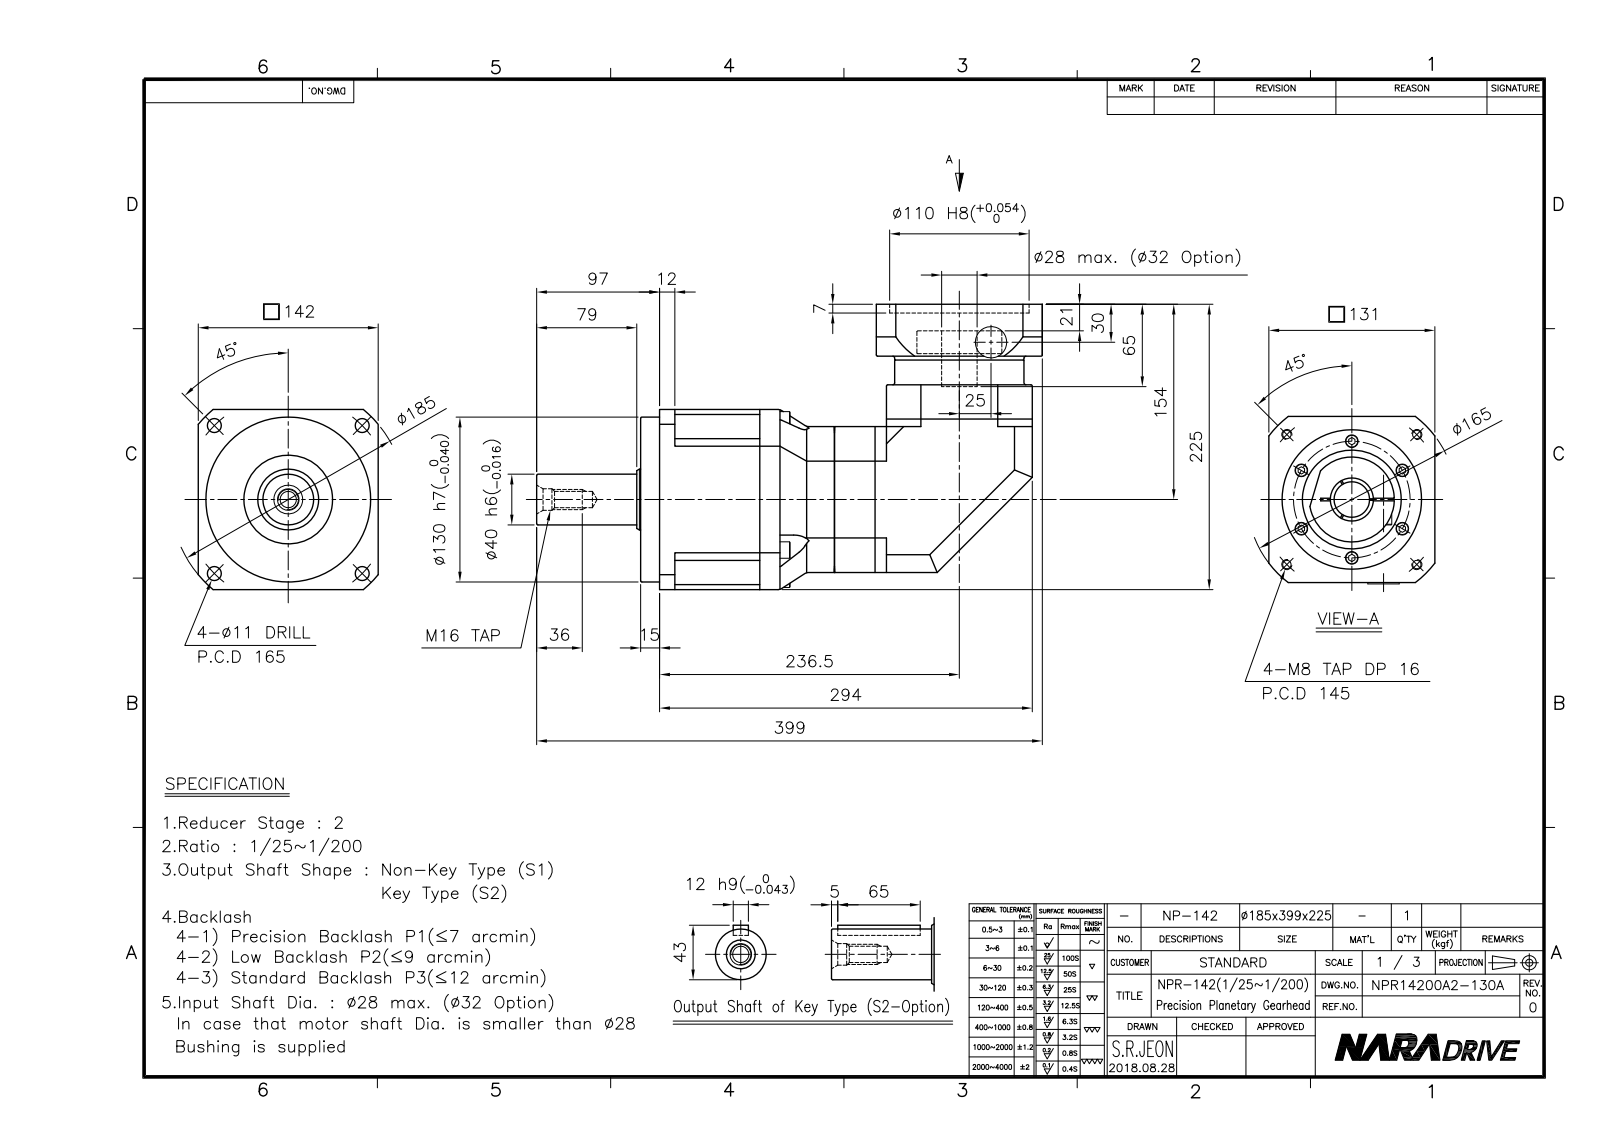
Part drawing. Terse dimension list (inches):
name: NPR14200A2-S1-130A
written by: Autodesk Inventor 2015 (AUTOMOTIVE_DESIGN)
unit: in
bodies: 2 solids, 714 faces (347 planar, 197 cylindrical, 170 other)
size: 15.709 × 8.858 × 5.591
volume: 250.1 in³; area: 601.8 in²
holes: 14× ⌀0.433, 10× ⌀0.26, 9× ⌀0.262, 8× ⌀0.163, 8× ⌀0.194, 8× ⌀0.217, 8× ⌀0.374, 4× ⌀0.335, 2× ⌀2.756, 1× ⌀0.354, 1× ⌀0.492, 1× ⌀0.545
bosses: 10× ⌀0.394, 10× ⌀0.236, 5× ⌀0.512, 5× ⌀0.315, 4× ⌀0.335, 4× ⌀0.197, 1× ⌀5.118, 1× ⌀4.016
rounds: 8× R0.039, 8× R0.197, 8× R0.591, 4× R0.02, 2× R3.248, 1× R0.276, 1× R2.549, 1× R2.559
face distances: 0.531, 5.059, 4.528, 5.591, 0.315, 4.843, 3.346, 1.614, 3.701, 0.354
hole spacings: 1.811, 4.037, 2.3, 2.313, 2.854, 3.253, 5.502, 0.711
